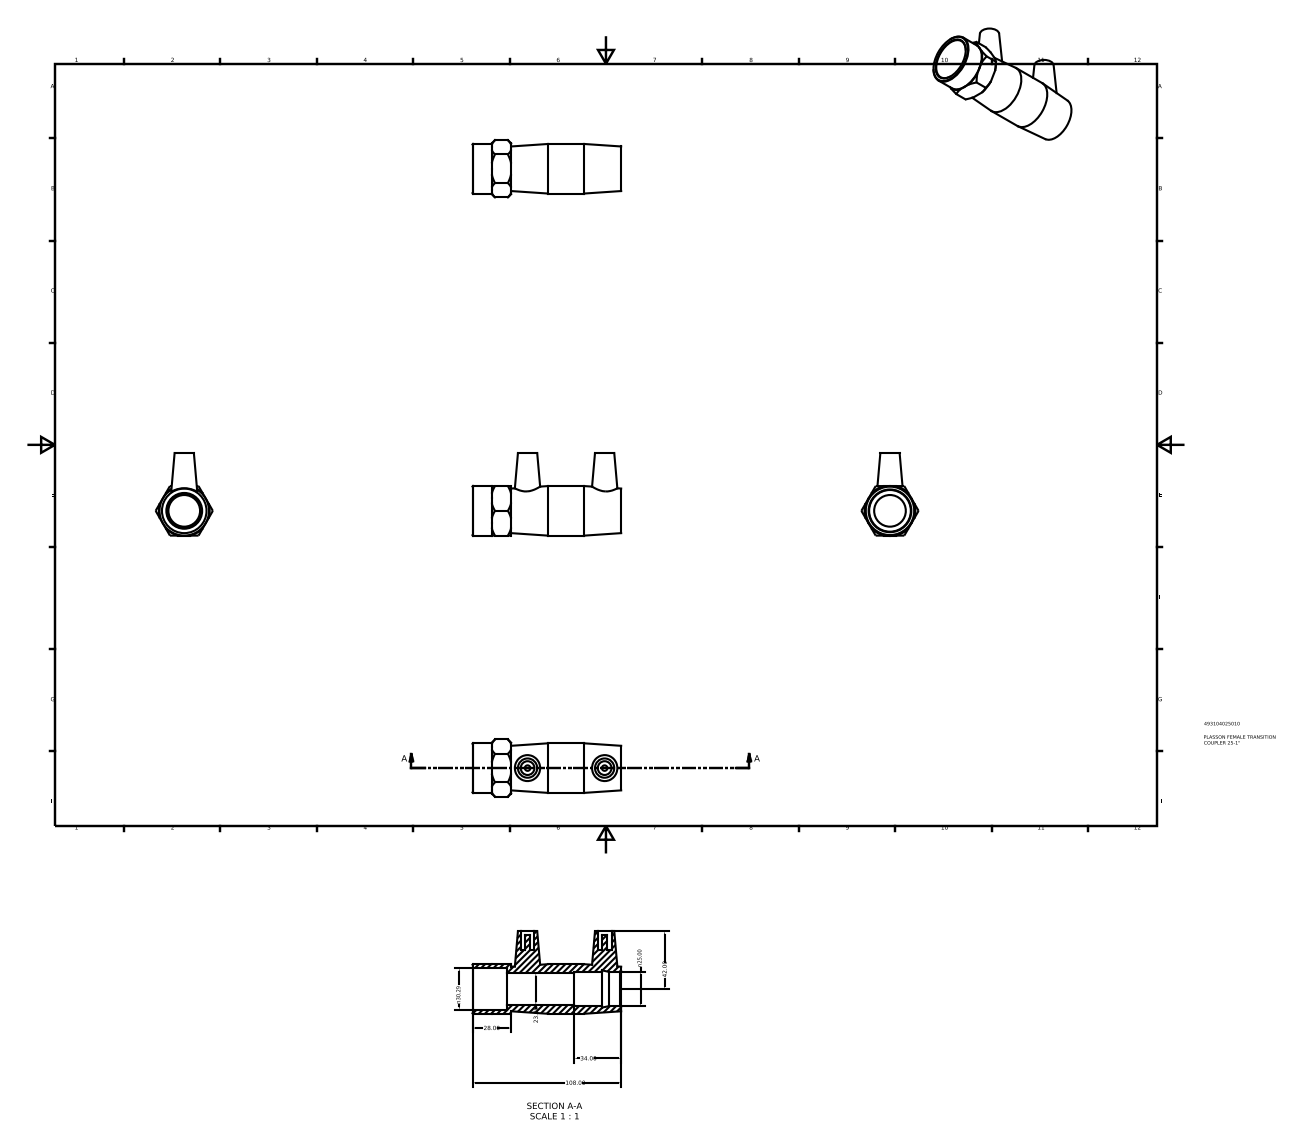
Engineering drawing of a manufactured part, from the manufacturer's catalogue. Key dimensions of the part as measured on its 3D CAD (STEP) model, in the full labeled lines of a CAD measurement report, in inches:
Part name (STEP PRODUCT): 493104025010
STEP written by: Autodesk Inventor 2015 (AUTOMOTIVE_DESIGN)
Units: inches
Bodies: 1 solid, 54 faces (24 planar, 10 cylindrical, 20 other)
Overall size (bounding box): 4.252 × 2.362 × 1.637
Volume: 3.631 in³ · Surface area: 39.74 in²
Round holes (diameter × count): ⌀0.394 ×2, ⌀0.906 ×1, ⌀0.984 ×1, ⌀1.193 ×1
Round bosses / shafts (diameter × count): ⌀0.157 ×2, ⌀1.417 ×1
Main face-to-face distances: 1.417, 3.26, 0.11, 3.15, 0.992, 1.102, 4.252, 0.551, 1.811, 2.362
Hole centre spacings: 2.205
